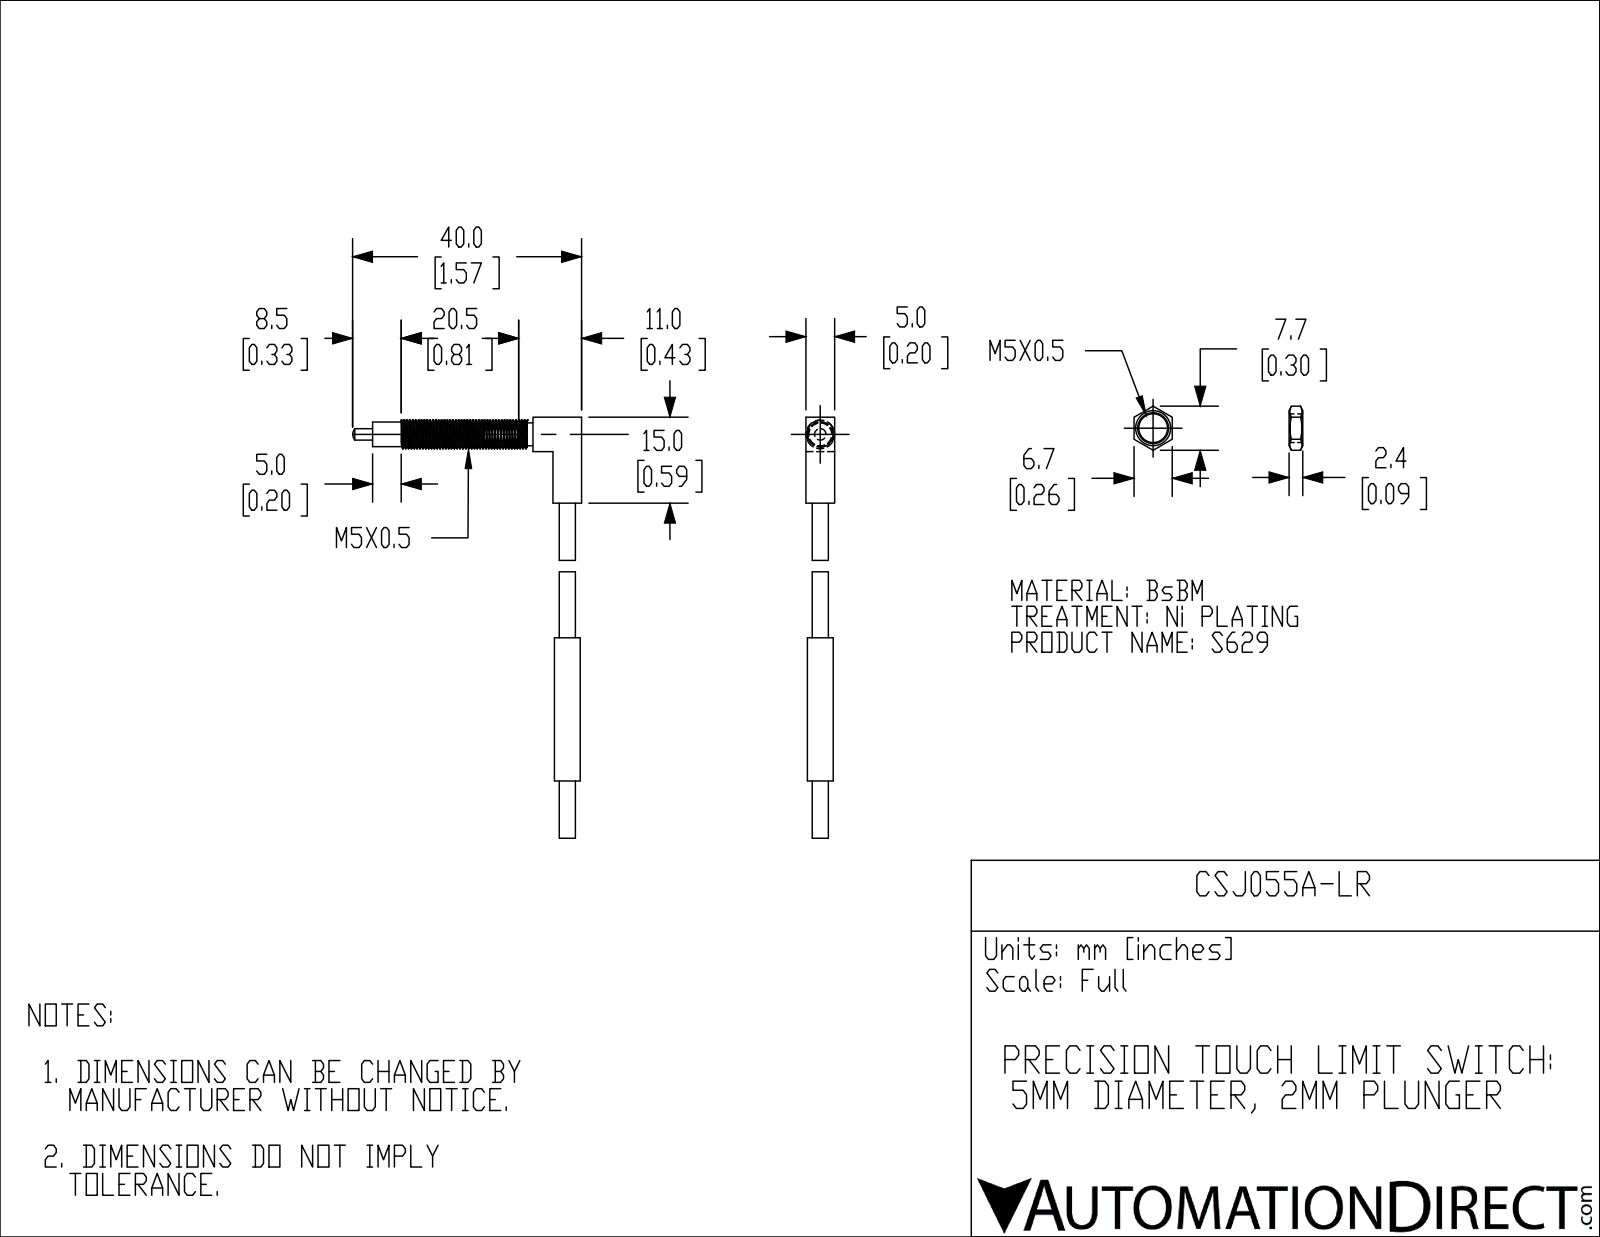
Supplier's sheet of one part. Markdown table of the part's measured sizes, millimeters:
| quantity | value |
| --- | --- |
| part name | CSJ055A-LR |
| STEP written by | SolidWorks 2018 (AUTOMOTIVE_DESIGN) |
| units | millimeters |
| bodies | 2 solids, 33 faces (22 planar, 8 cylindrical, 3 other) |
| overall size | 73.5 × 40 × 5 |
| volume | 1 593 mm³ |
| surface area | 1 548 mm² |
| round bosses / shafts (diameter × count) | 5 × 1, 4.5 × 1, 4.3 × 1, 4 × 1, 2.8 × 1, 2 × 1 |
| main face-to-face distances | 5, 4.7, 6, 15, 8.5, 36.5, 9, 3.5, 38.5, 25 |
